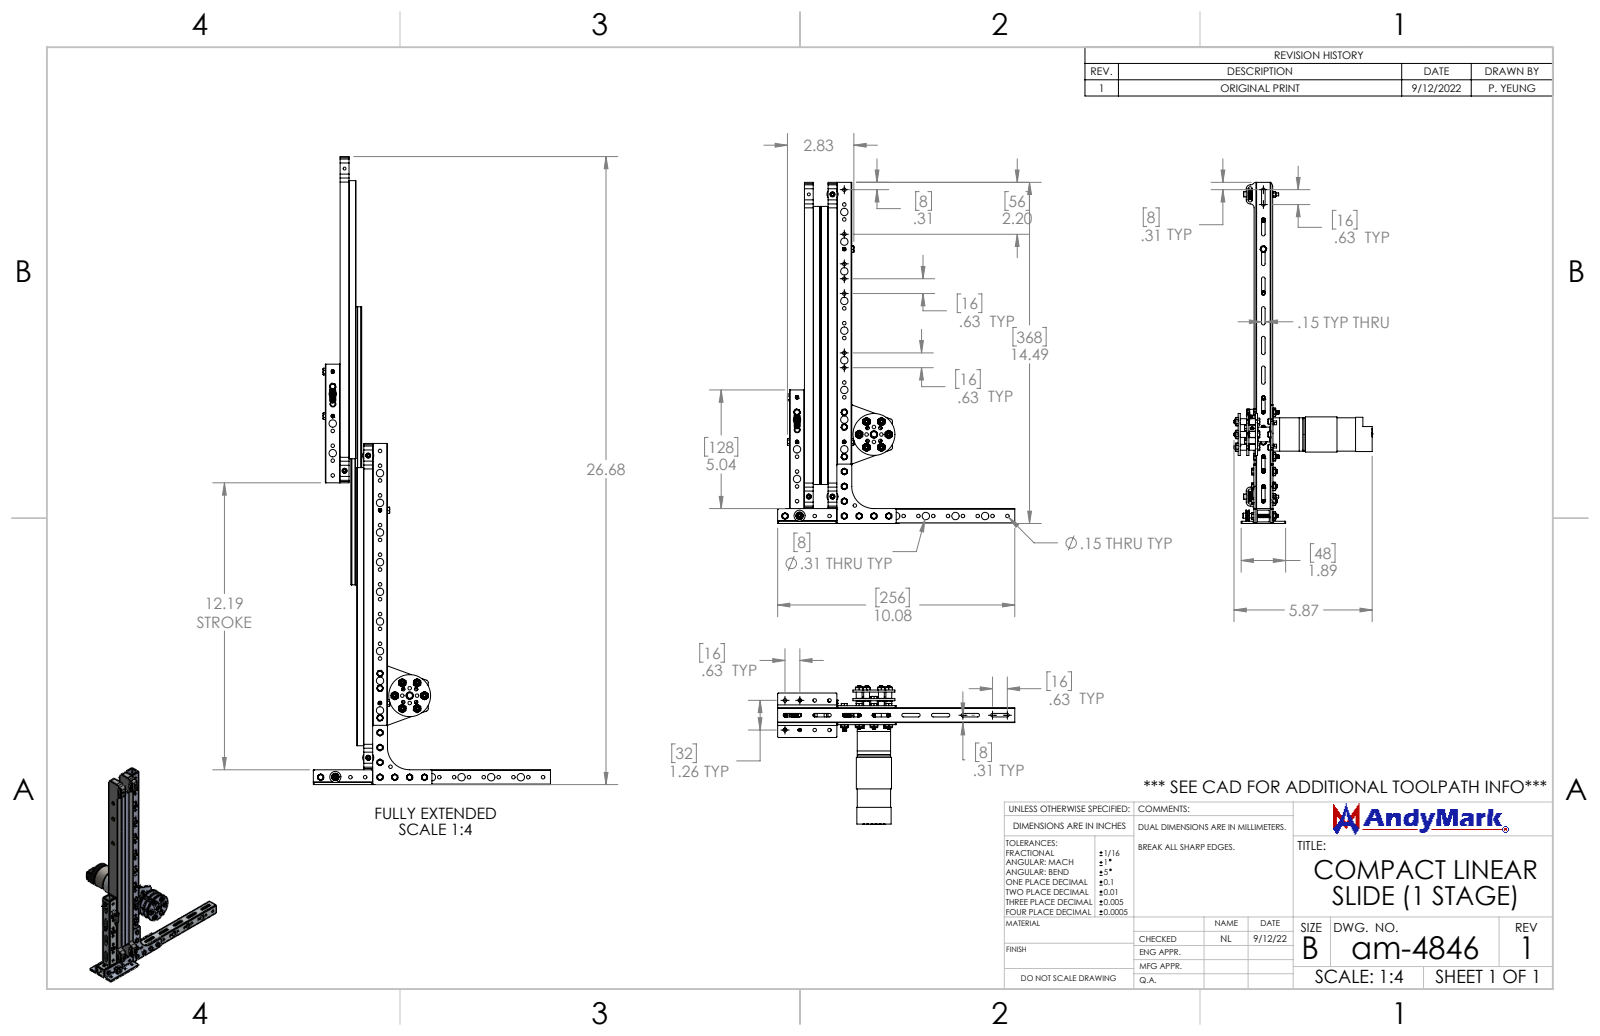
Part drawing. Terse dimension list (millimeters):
name: am-1669 0.141ID 0.25OD 0.266 Long Aluminum Spacer; Pulley Holder Assy_Add a Stage Pulley Holder; am-4610b NeveRest Orbital 14 Gearmotor; am-4837 SAR330 Aluminum Slide_Retracted (+8 more)
written by: SolidWorks 2022 (AUTOMOTIVE_DESIGN)
unit: mm
bodies: 218 solids, 10141 faces (1310 planar, 4596 cylindrical, 4235 other)
size: 368 × 256 × 149.4
volume: 418 400 mm³; area: 277 900 mm²
holes: 69× ⌀3.8, 54× ⌀2.9, 24× ⌀8, 18× ⌀2.8, 18× ⌀4.9, 12× ⌀3.8, 10× ⌀2.5, 8× ⌀3.2, 7× ⌀3.6, 5× ⌀3, 4× ⌀2.7, 4× ⌀3.2
bosses: 25× ⌀3.5, 12× ⌀5.5, 9× ⌀3, 7× ⌀6.4, 6× ⌀2.4, 4× ⌀12, 4× ⌀5.5, 4× ⌀4.7
rounds: 40× R0.2, 38× R1.9, 34× R1.6, 18× R1.5, 13× R1, 12× R0.3, 12× R0.6, 12× R4.2
face distances: 16, 14.4, 1.6, 2, 18, 25.5, 3.6, 16.4, 12.8, 2.3
hole spacings: 32, 16, 64, 48, 96, 8, 24, 56
